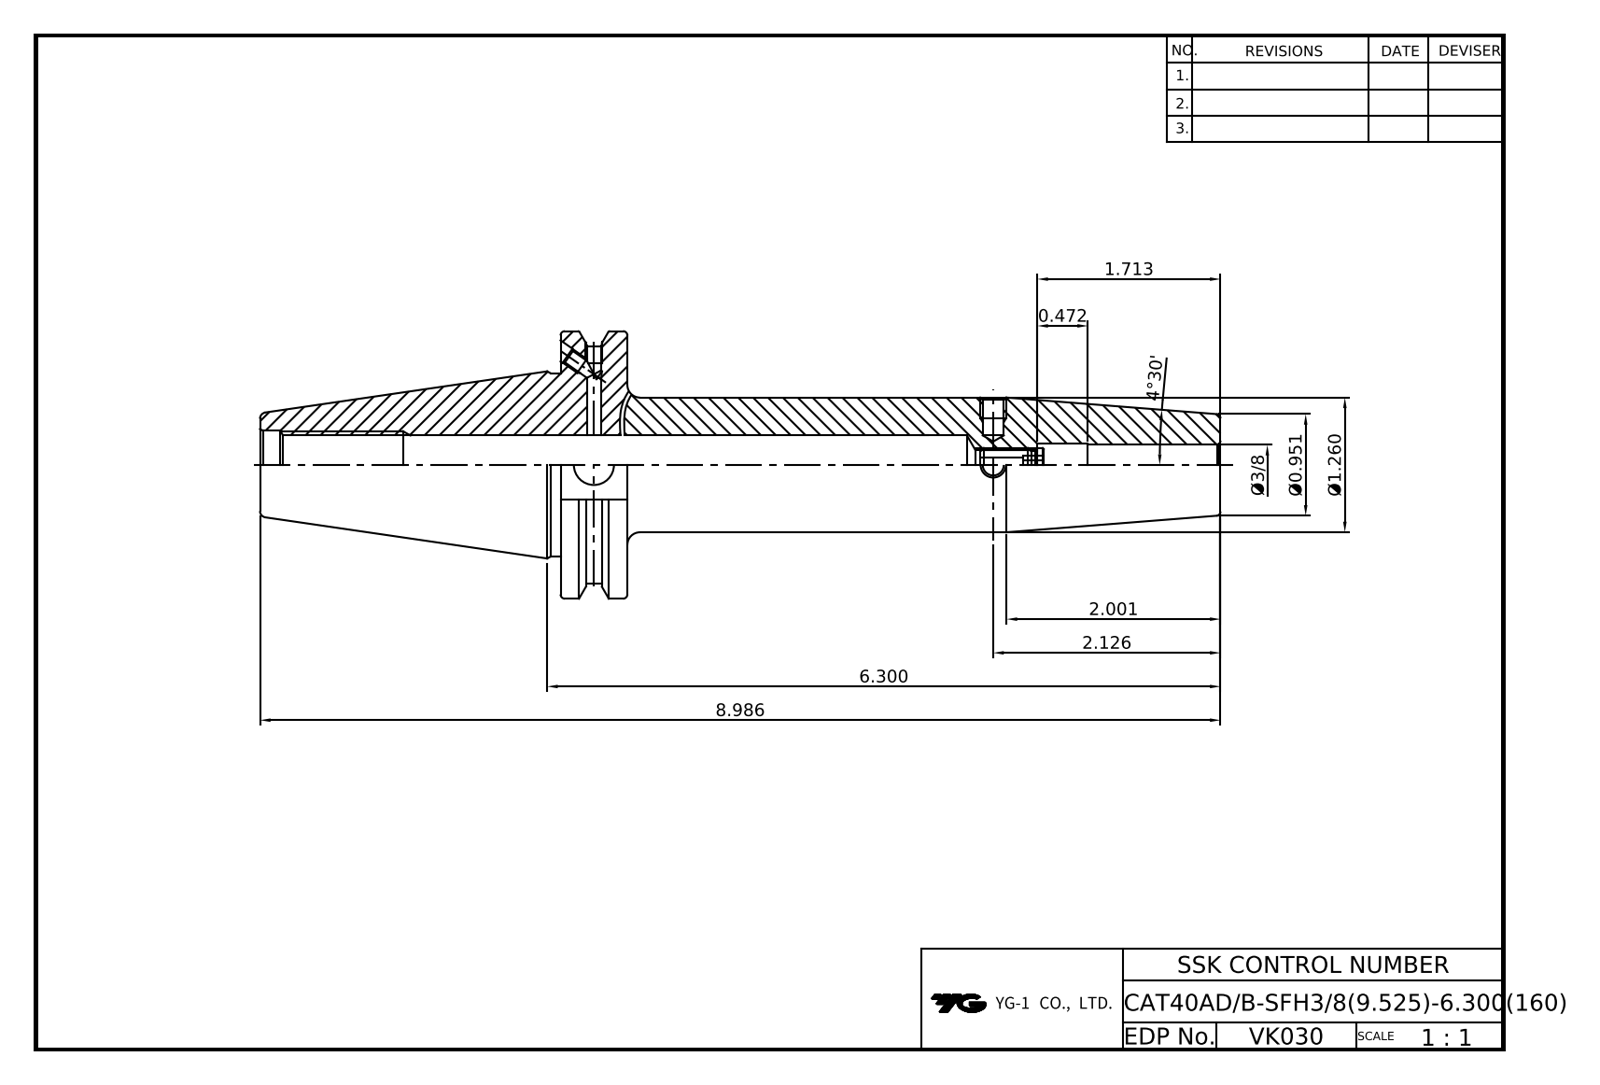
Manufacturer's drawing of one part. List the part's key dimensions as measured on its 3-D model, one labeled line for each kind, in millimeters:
Part name (STEP PRODUCT): LO-CAT40ADB-SFH9.525-160
STEP written by: Autodesk Inventor 2022 (AUTOMOTIVE_DESIGN)
Units: millimetres
Bodies: 1 solid, 87 faces (37 planar, 29 cylindrical, 21 other)
Overall size (bounding box): 228.25 × 63.5 × 61.09
Volume: 190 242 mm³ · Surface area: 38 883 mm²
Round holes (diameter × count): ⌀3.24 ×4, ⌀4 ×2, ⌀4.2 ×2, ⌀9.53 ×2, ⌀6.92 ×1, ⌀10.72 ×1, ⌀13 ×1, ⌀13.39 ×1, ⌀16.3 ×1
Round bosses / shafts (diameter × count): ⌀63.5 ×1, ⌀43.6 ×1, ⌀32 ×1
Partial cylindrical surfaces — rounded edges, fillets, slot ends (radius × count): R28.15 ×1
Main face-to-face distances: 15.88, 156.83, 140.95, 47.6, 16.38, 71.42, 87.3, 228.25, 77.47, 6.05
